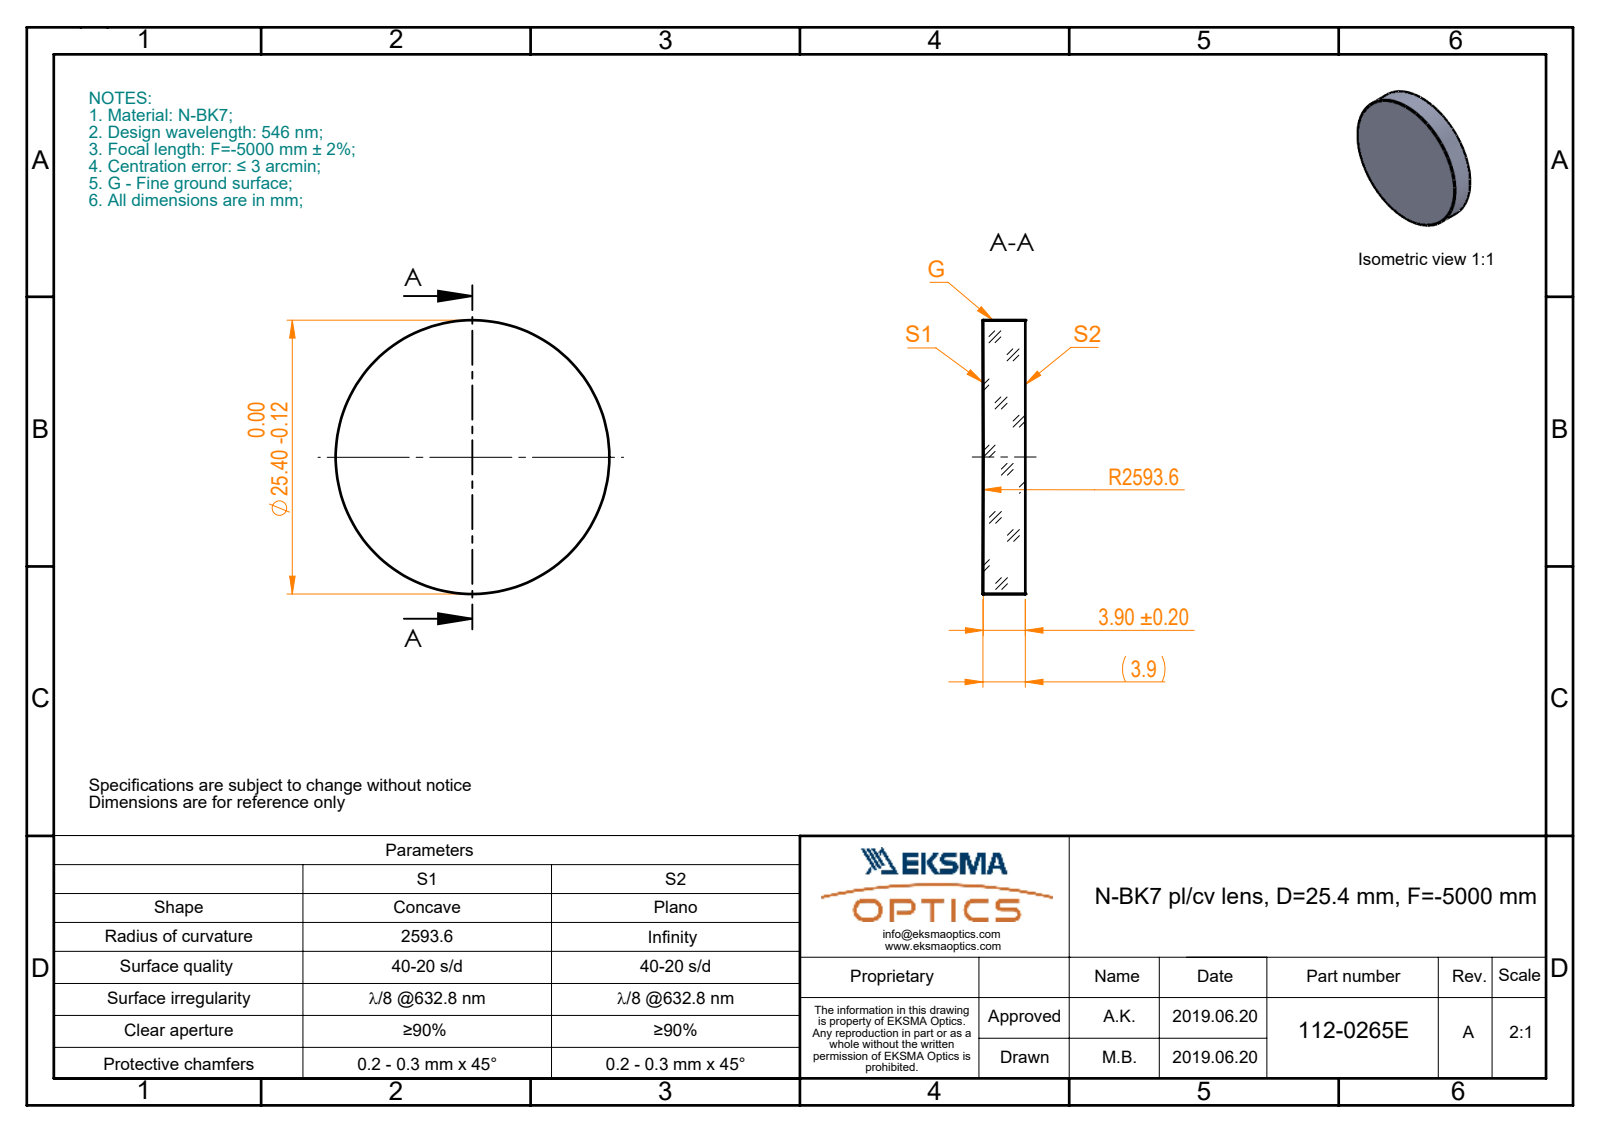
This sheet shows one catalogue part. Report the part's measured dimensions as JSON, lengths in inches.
{"part_name": "112-0265E BK7 pl-cv 25.4 F-5000", "step_written_by": "SolidWorks 2017 (CONFIG_CONTROL_DESIGN)", "units": "inches", "bodies": {"solids": 1, "faces": 5, "planar": 1, "cylindrical": 2, "other": 2}, "overall_size": [1, 1, 0.155], "volume_in3": 0.121, "surface_area_in2": 2.057, "round_bosses_or_shafts": [[1, 1]]}
